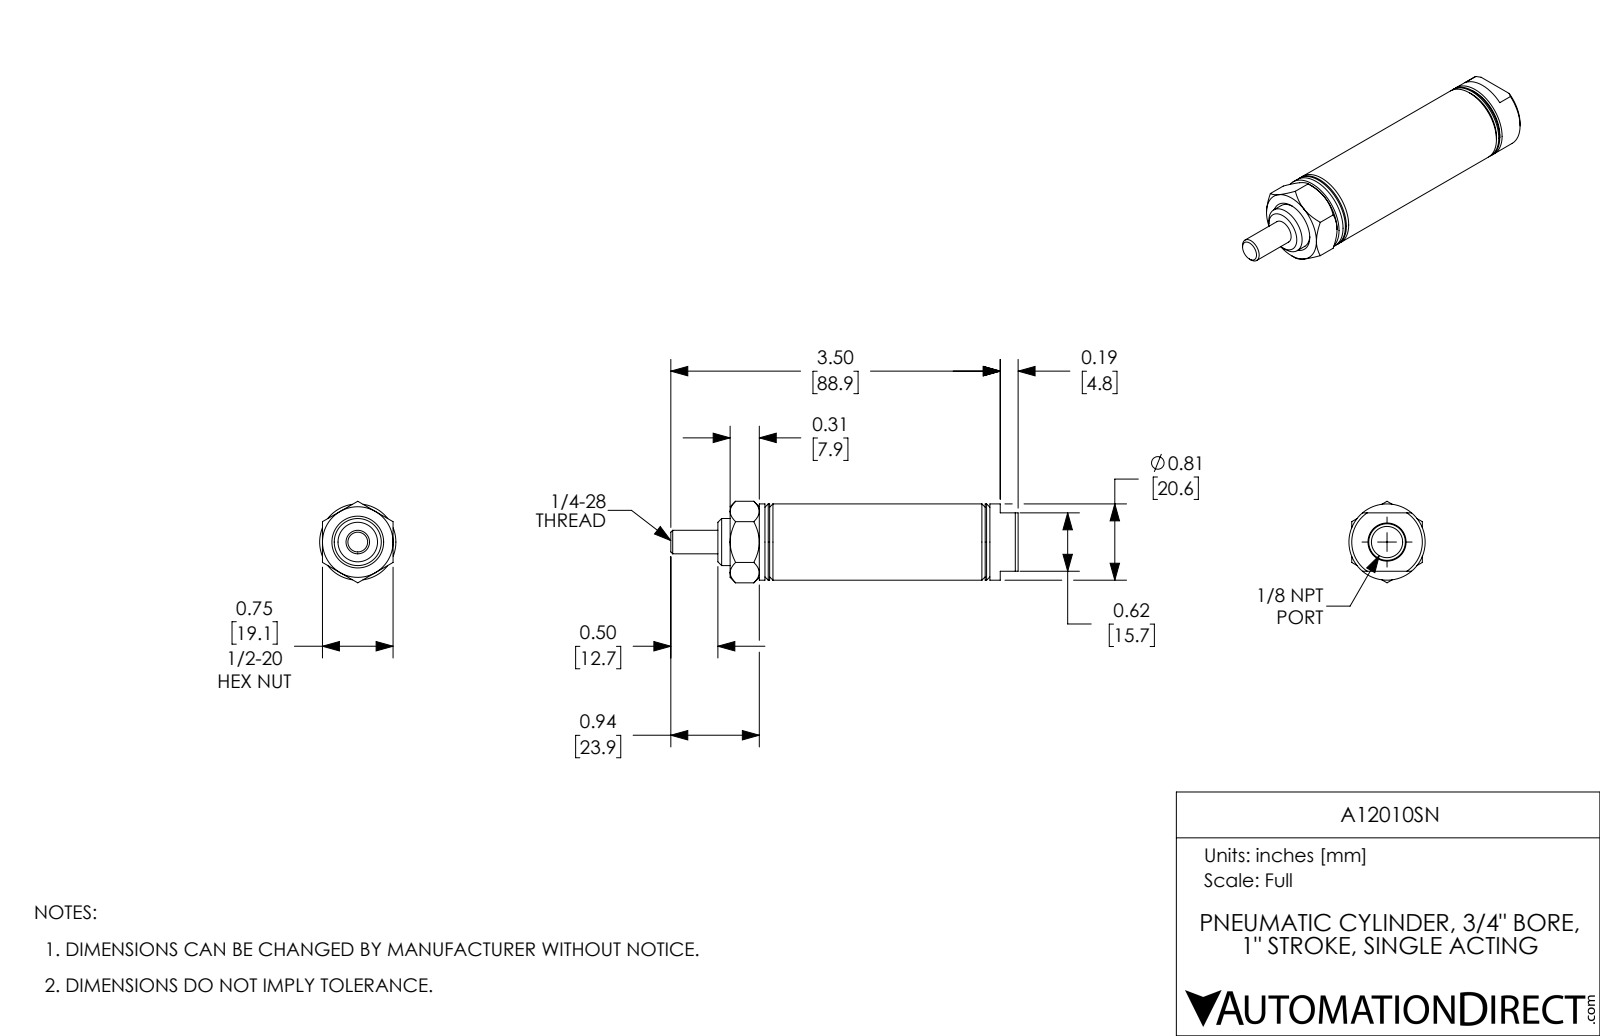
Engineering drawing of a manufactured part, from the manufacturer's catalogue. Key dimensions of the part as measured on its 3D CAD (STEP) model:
Part name (STEP PRODUCT): A12010SN; A12010SN_Mounting Nut_D-98; A12010SN-Rod; A12010SN-MainBody
STEP written by: SolidWorks 2017 (AUTOMOTIVE_DESIGN)
Units: inches
Bodies: 3 solids, 82 faces (25 planar, 24 cylindrical, 33 other)
Overall size (bounding box): 3.69 × 0.866 × 0.81
Volume: 1.138 in³ · Surface area: 20.61 in²
Round holes (diameter × count): ⌀0.25 ×1, ⌀0.332 ×1, ⌀0.5 ×1, ⌀0.75 ×1
Round bosses / shafts (diameter × count): ⌀0.81 ×1
Main face-to-face distances: 2.125, 0.5, 1, 1.625, 1.5, 0.625, 0.625, 1.125, 2.125, 2.75
